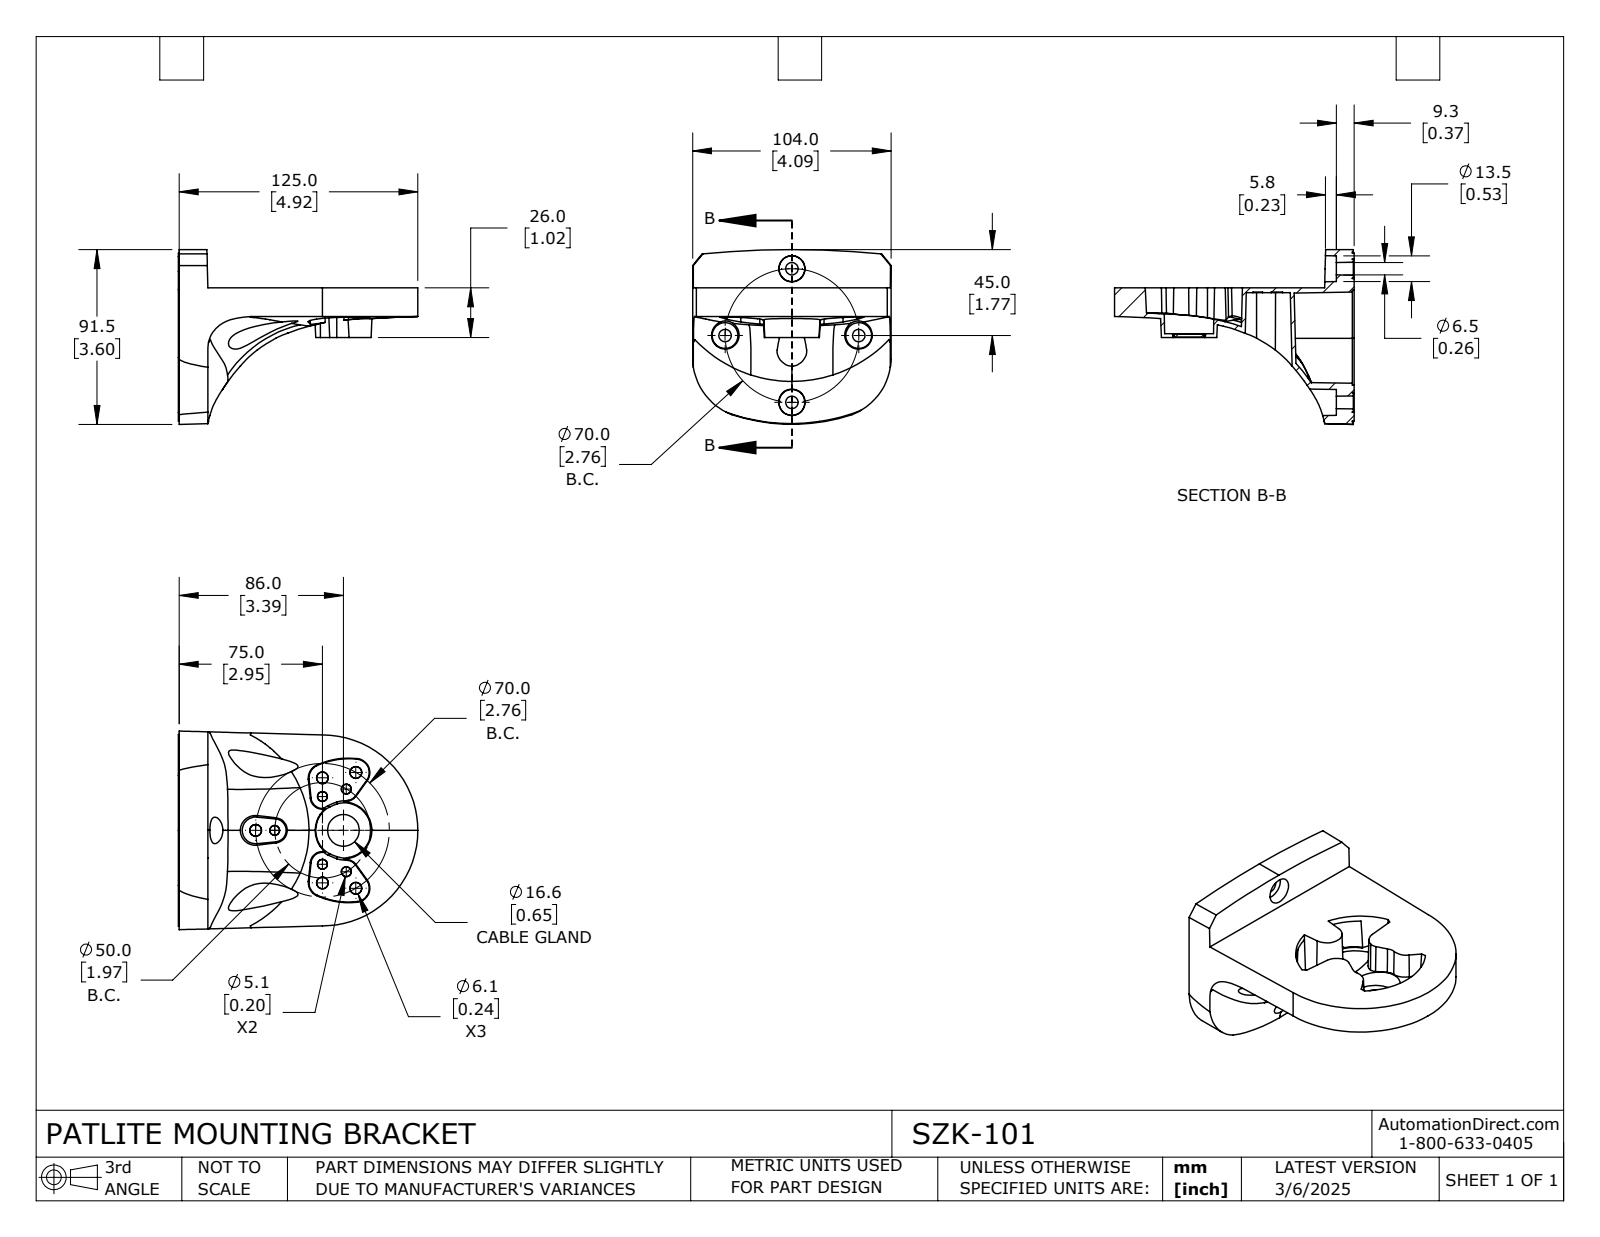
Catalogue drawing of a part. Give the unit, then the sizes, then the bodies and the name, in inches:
Units: inches
Overall size (bounding box): 4.941 × 4.094 × 3.602
Round holes (diameter × count): ⌀0.406 ×4, ⌀0.654 ×1
Partial cylindrical surfaces — rounded edges, fillets, slot ends (radius × count): R0.965 ×2, R1.969 ×1
Main face-to-face distances: 0.098, 0.02, 0.366, 0.346, 0.925, 1.024, 0.081, 0.039, 0.327, 0.081
Hole centre spacings: 1.949, 2.756
Volume: 13.26 in³ · Surface area: 98.7 in²
Bodies: 1 solid, 232 faces (68 planar, 13 cylindrical, 151 other)
Part name (STEP PRODUCT): SZK-101
STEP written by: SolidWorks 2024 (CONFIG_CONTROL_DESIGN)
